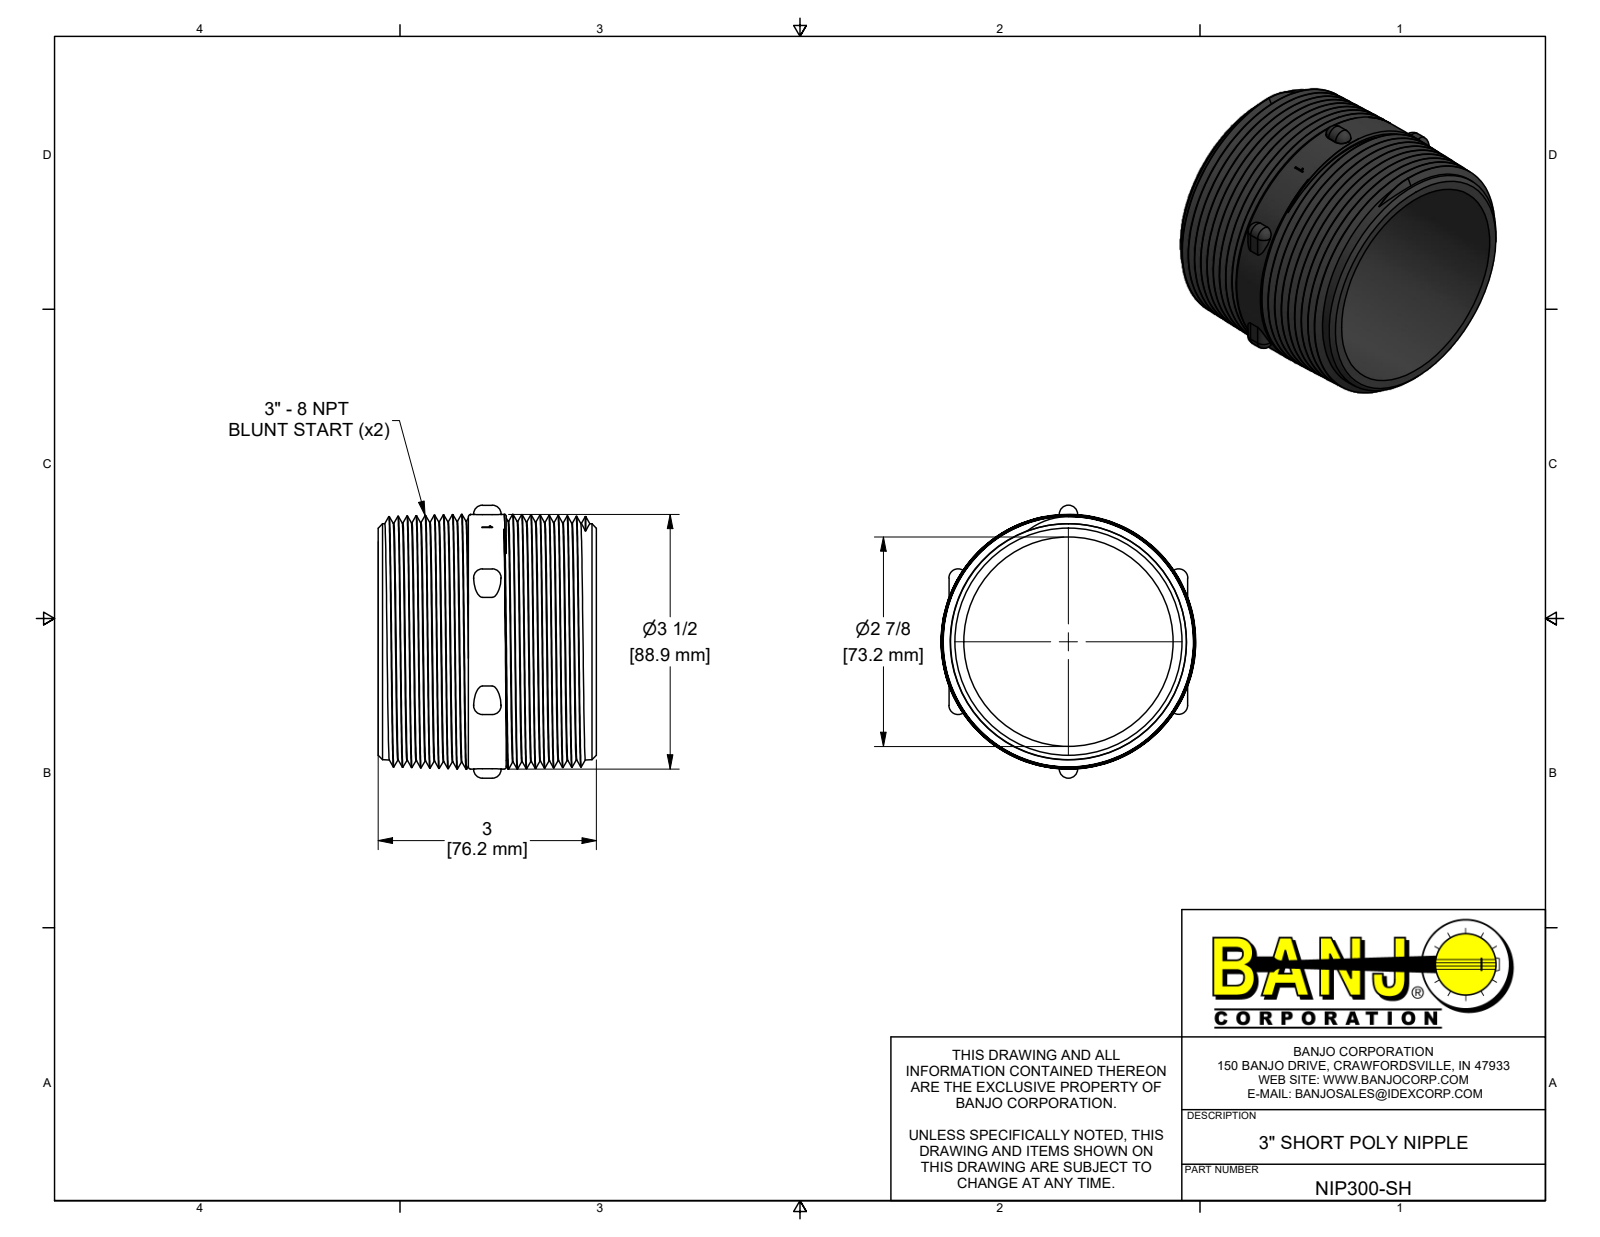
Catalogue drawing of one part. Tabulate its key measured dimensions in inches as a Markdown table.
| quantity | value |
| --- | --- |
| part name | NIP300-SH |
| STEP written by | Autodesk Inventor 2019 (AUTOMOTIVE_DESIGN) |
| units | inches |
| bodies | 1 solid, 111 faces (30 planar, 29 cylindrical, 52 other) |
| overall size | 107.258 × 3.75 × 3.5 |
| volume | 7.476 in³ |
| surface area | 2 260 in² |
| round holes (diameter × count) | 2.88 × 1 |
| round bosses / shafts (diameter × count) | 3.5 × 1 |
| partial cylindrical surfaces (radius × count) | 0.12 × 8, 0.125 × 6, 0.908 × 1, 1.74 × 1 |
| main face-to-face distances | 3, 1.24, 1.76, 0.52, 3.281, 1.516, 1.765, 0.25, 1.313, 1.687 |
